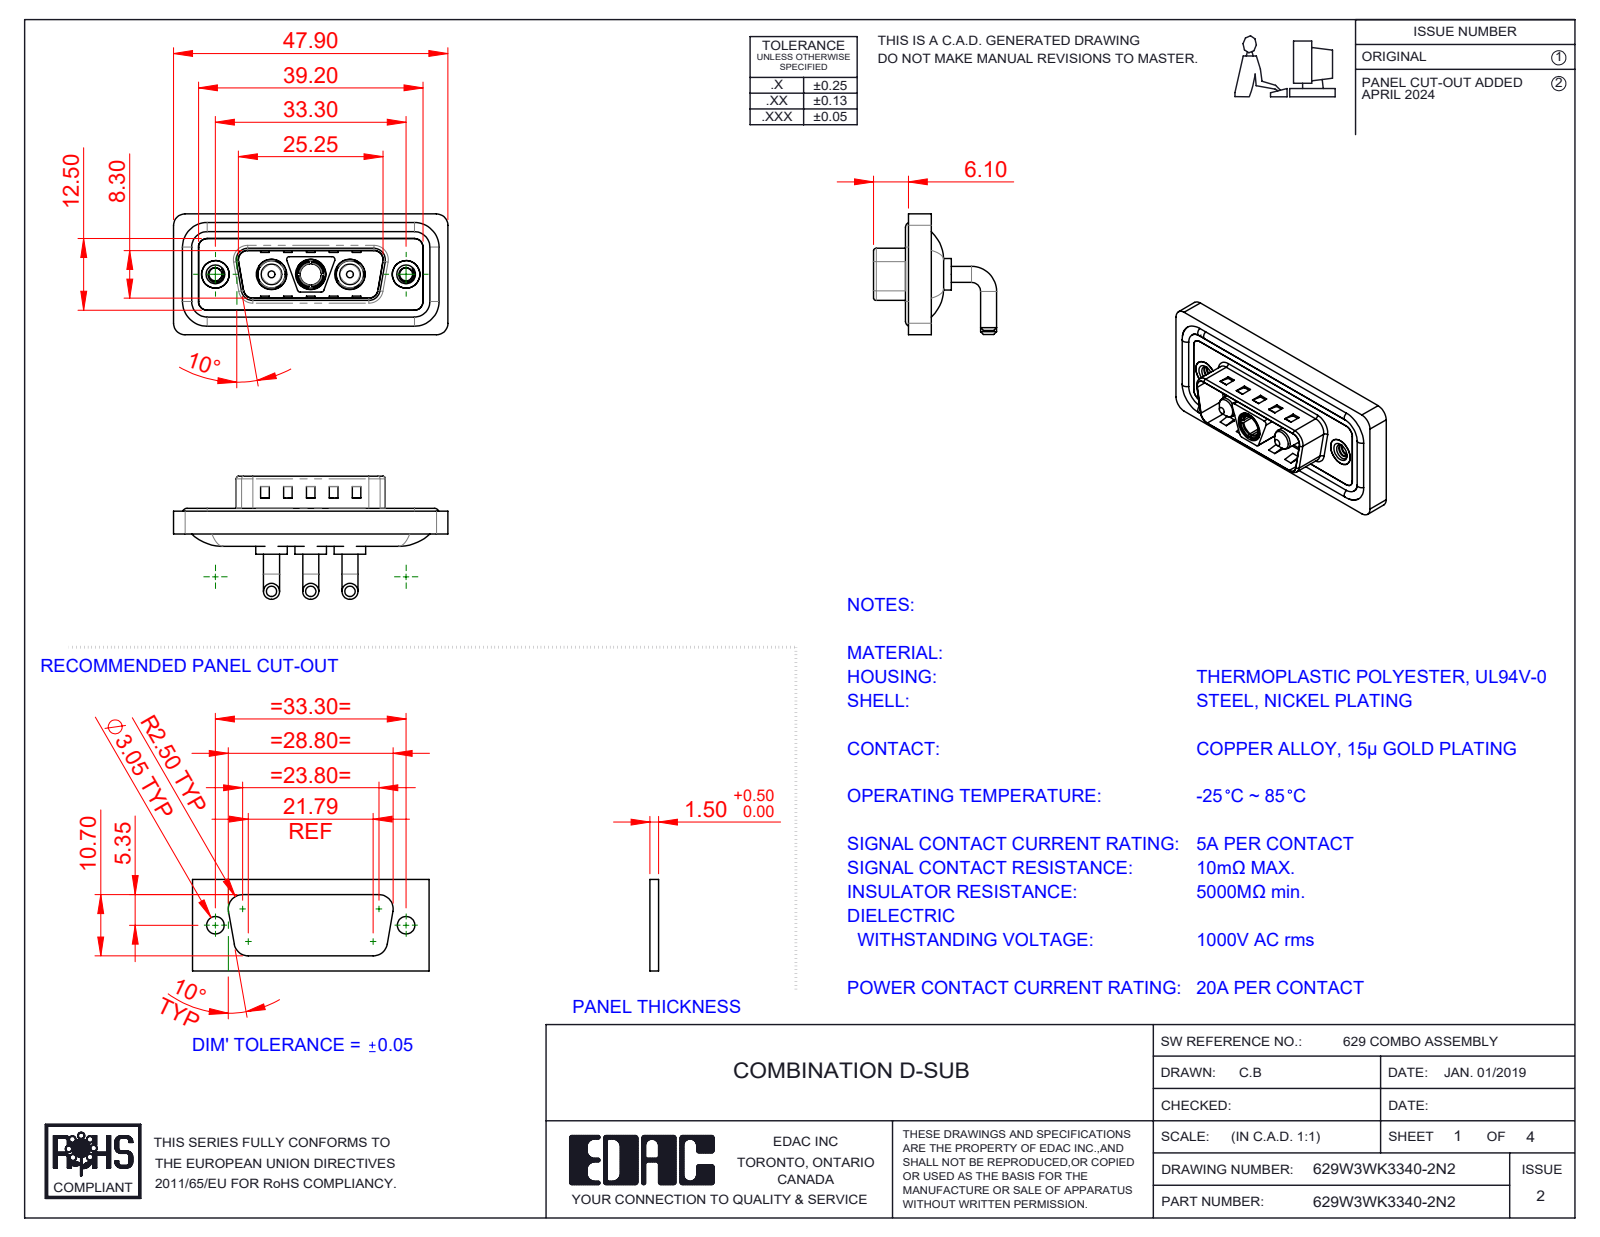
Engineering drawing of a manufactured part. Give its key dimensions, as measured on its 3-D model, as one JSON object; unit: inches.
{"part_name": "Power Socket_20A RA; 629Combo Threaded Rivet_2; 629Combo Waterproof Housing_15 Contacts; 629Combo Housing_3WK3 (+4 more)", "step_written_by": "SolidWorks 2023 (CONFIG_CONTROL_DESIGN)", "units": "inches", "bodies": {"solids": 13, "faces": 621, "planar": 231, "cylindrical": 256, "other": 134}, "overall_size": [1.886, 0.846, 0.831], "volume_in3": 0.36, "surface_area_in2": 14.59, "round_holes": [[0.191, 3], [0.209, 3], [0.089, 2], [0.157, 2], [0.189, 2], [0.197, 2], [0.146, 1]], "round_bosses_or_shafts": [[0.11, 6], [0.063, 4], [0.217, 3], [0.205, 3], [0.187, 3], [0.148, 3], [0.193, 2], [0.142, 2]], "partial_cylinders_radius": [[0.079, 20], [0.059, 18], [0.02, 12], [0.063, 8], [0.01, 4], [0.024, 4], [0.026, 4], [0.035, 4]], "face_to_face_distances": [0.016, 0.114, 0.031, 0.043, 0.083, 0.063, 0.122, 0.098, 0.177, 0.146], "hole_center_spacings": [0.27, 0.386, 0.656, 0.925, 0.539, 1.311]}
